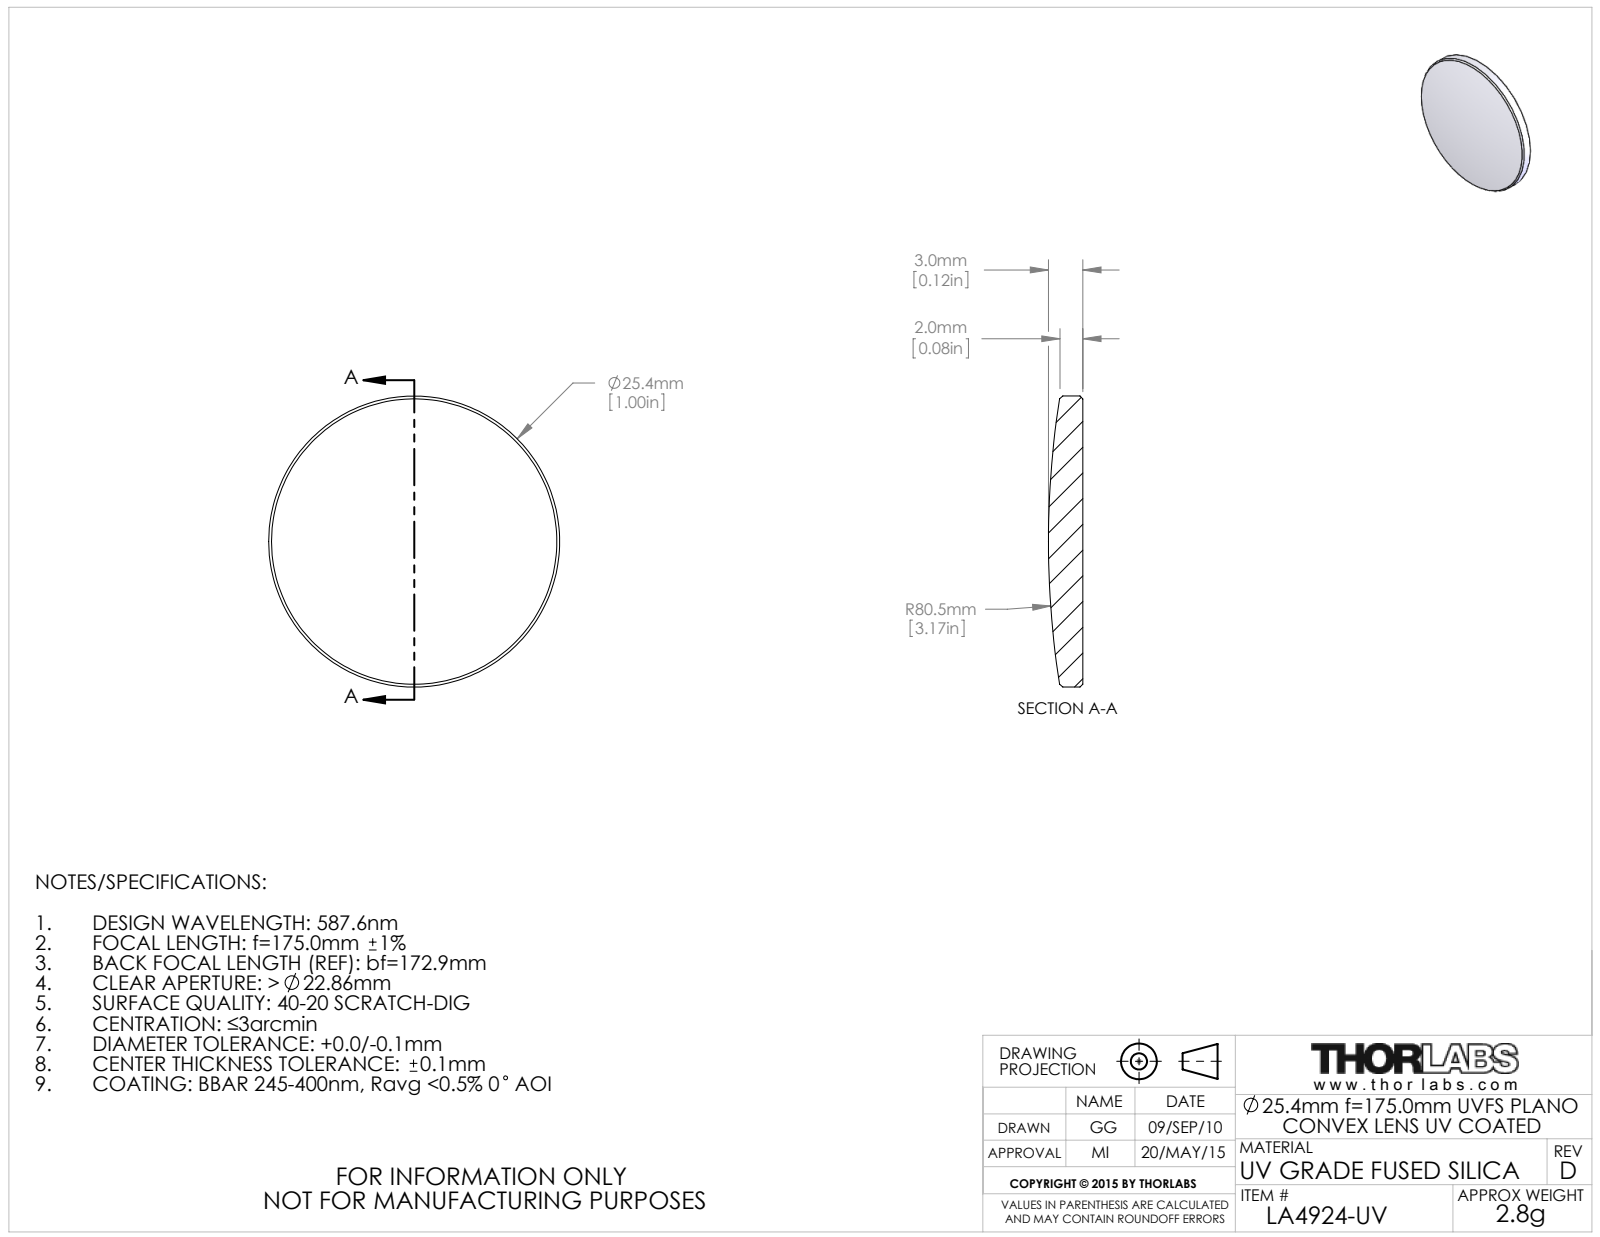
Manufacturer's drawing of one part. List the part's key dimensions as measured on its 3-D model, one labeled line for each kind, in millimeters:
Part name (STEP PRODUCT): 4285-E0W
STEP written by: SolidWorks 2014 (CONFIG_CONTROL_DESIGN)
Units: millimetres
Bodies: 1 solid, 9 faces (1 planar, 2 cylindrical, 6 other)
Overall size (bounding box): 25.4 × 25.4 × 3
Volume: 1 263 mm³ · Surface area: 1 155 mm²
Round bosses / shafts (diameter × count): ⌀25.4 ×1
